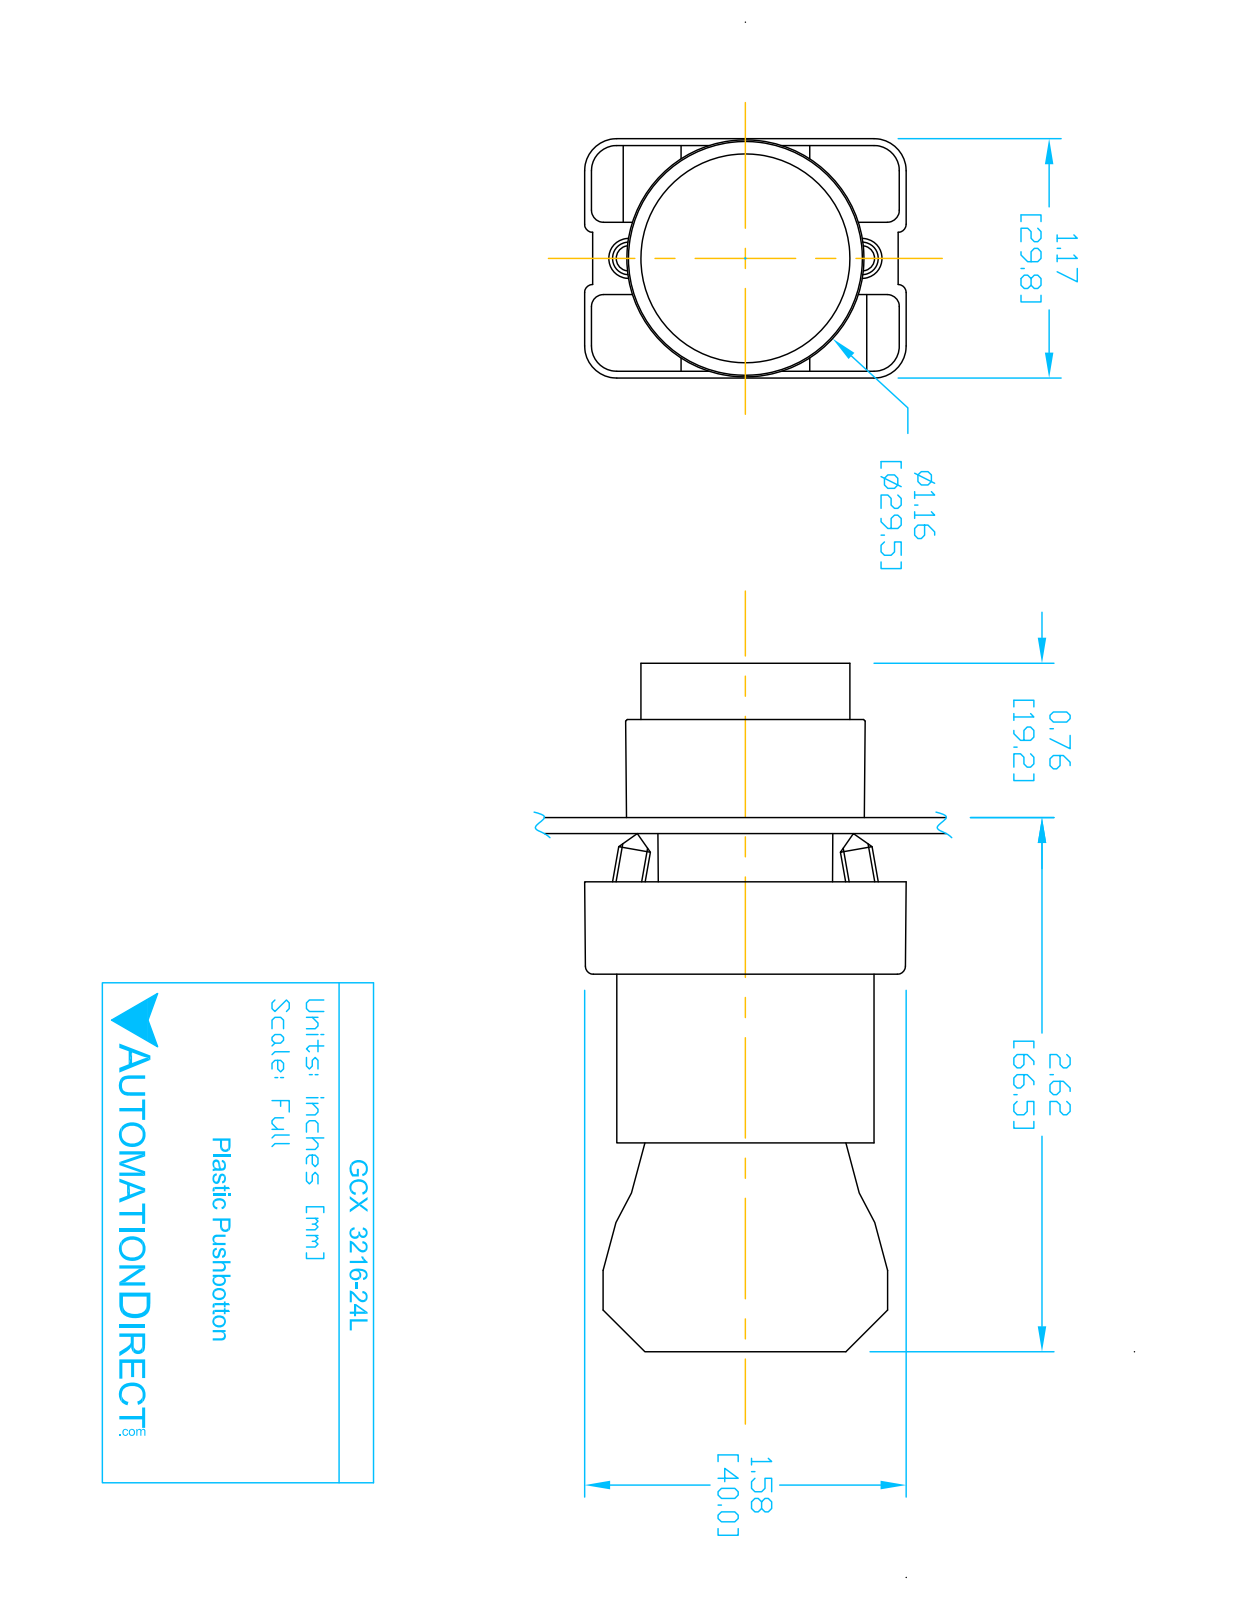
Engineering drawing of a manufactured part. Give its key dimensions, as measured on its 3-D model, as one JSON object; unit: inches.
{"part_name": "ECX1050; GCX3216L OPERATOR; GCX3216-24L; ecx1040 (+1 more)", "step_written_by": "SolidWorks 2016 (AUTOMOTIVE_DESIGN)", "units": "inches", "bodies": {"solids": 7, "faces": 425, "planar": 250, "cylindrical": 144, "other": 31}, "overall_size": [3.319, 1.581, 1.177], "volume_in3": 2.721, "surface_area_in2": 36.32, "round_holes": [[0.079, 2], [0.124, 2], [0.13, 2], [0.087, 1], [0.197, 1], [0.469, 1], [0.878, 1], [0.888, 1], [1.024, 1]], "round_bosses_or_shafts": [[0.157, 4], [1.175, 1], [1.004, 1], [0.945, 1], [0.856, 1], [0.78, 1], [0.504, 1]], "partial_cylinders_radius": [[0.059, 24], [0.041, 12], [0.124, 12], [0.157, 12], [0.039, 8], [0.128, 2], [0.02, 1], [0.063, 1]], "face_to_face_distances": [0.827, 0.579, 1.171, 2.02, 1.193, 0.031, 0.033, 0.573, 1.165, 0.593], "hole_center_spacings": [0.236, 0.544, 0.472, 0.49]}
